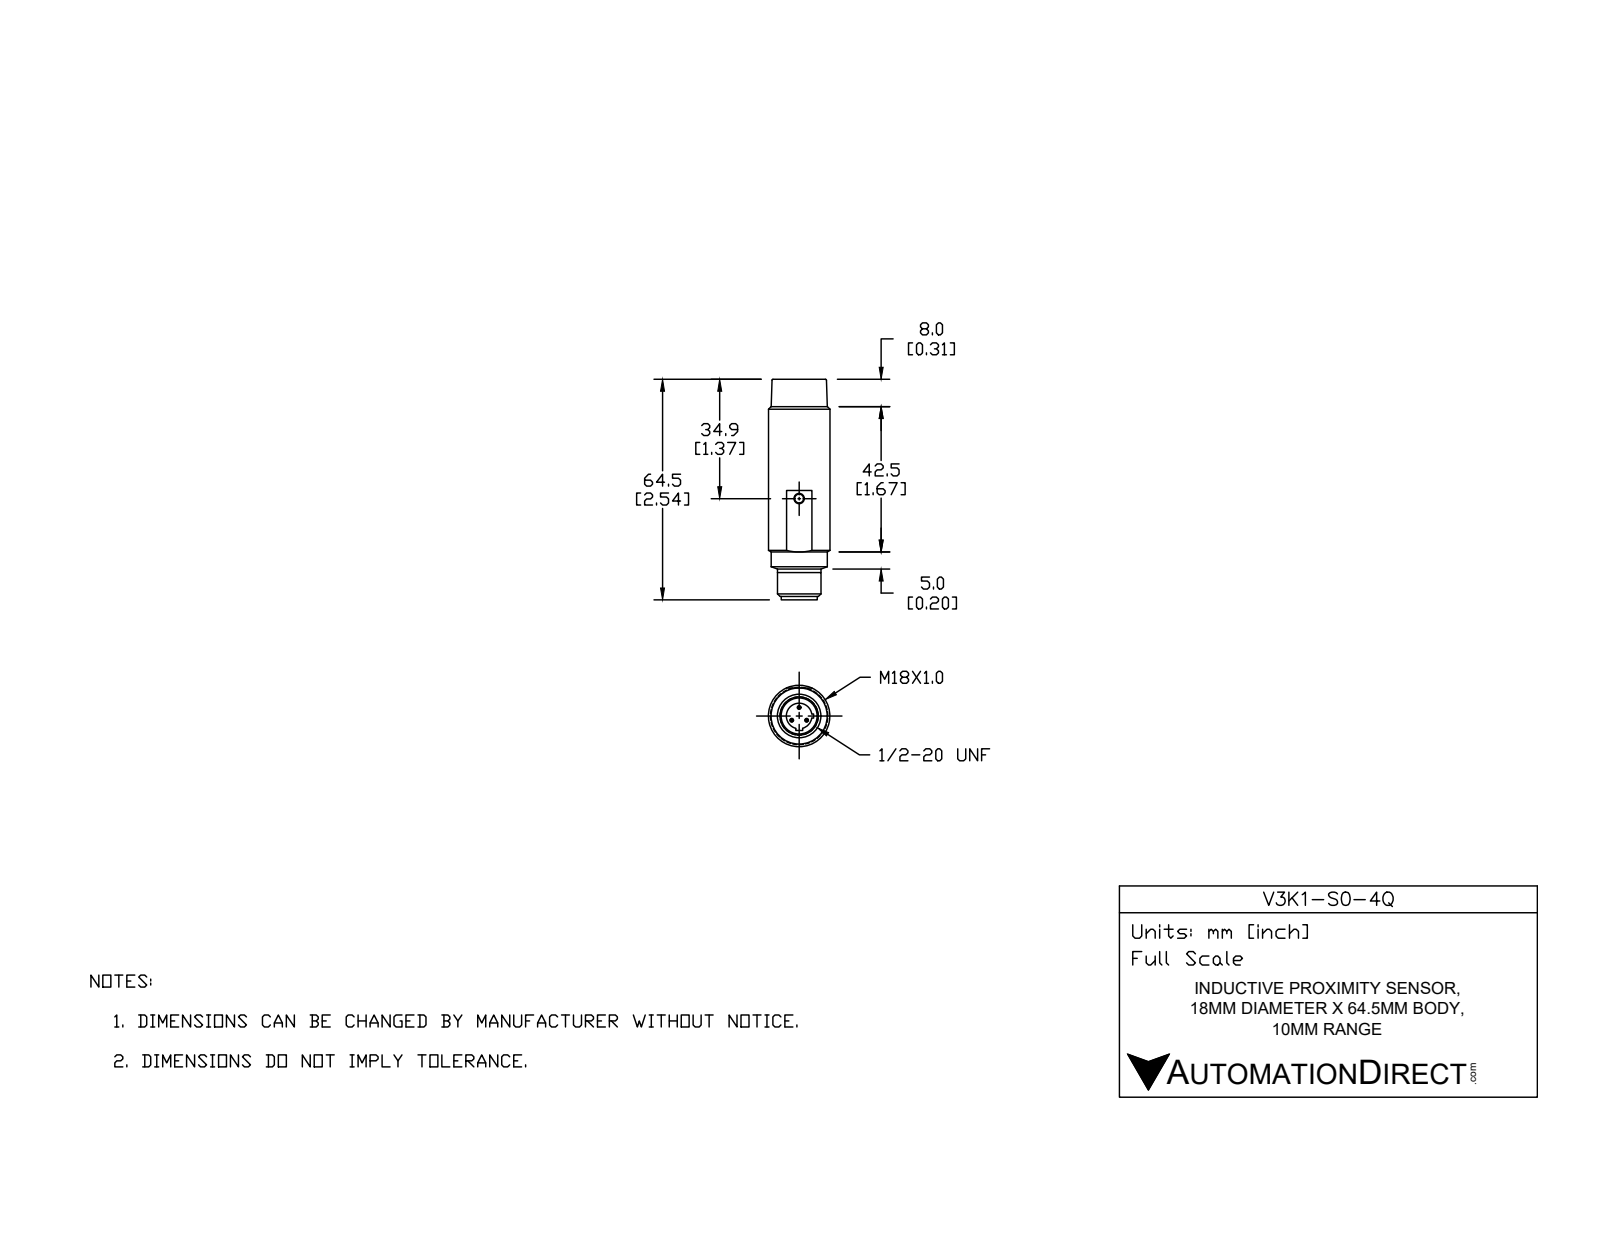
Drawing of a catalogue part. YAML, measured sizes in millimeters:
part_name: "V3K1_4Q_fig"
step_written_by: "ST-DEVELOPER v16.7 (AUTOMOTIVE_DESIGN)"
units: millimeters
bodies: {solids: 3, faces: 53, planar: 25, cylindrical: 17, other: 11}
overall_size: [64.5, 18, 18]
volume: 14145
surface_area: 4372
round_holes:
  - {diameter: 1, count: 3}
  - {diameter: 2.6, count: 1}
  - {diameter: 7.5, count: 1}
  - {diameter: 9.5, count: 1}
round_bosses_or_shafts:
  - {diameter: 0.98, count: 3}
  - {diameter: 18, count: 1}
  - {diameter: 16.4, count: 1}
  - {diameter: 12.7, count: 1}
  - {diameter: 10.5, count: 1}
  - {diameter: 9.55, count: 1}
  - {diameter: 9.4, count: 1}
face_to_face_distances: [57.4, 64.5, 7.1, 1, 63.5, 6.1, 12.4, 1.2, 7.6, 6.4]
hole_center_spacings: [2.5, 4.33, 4.34]
